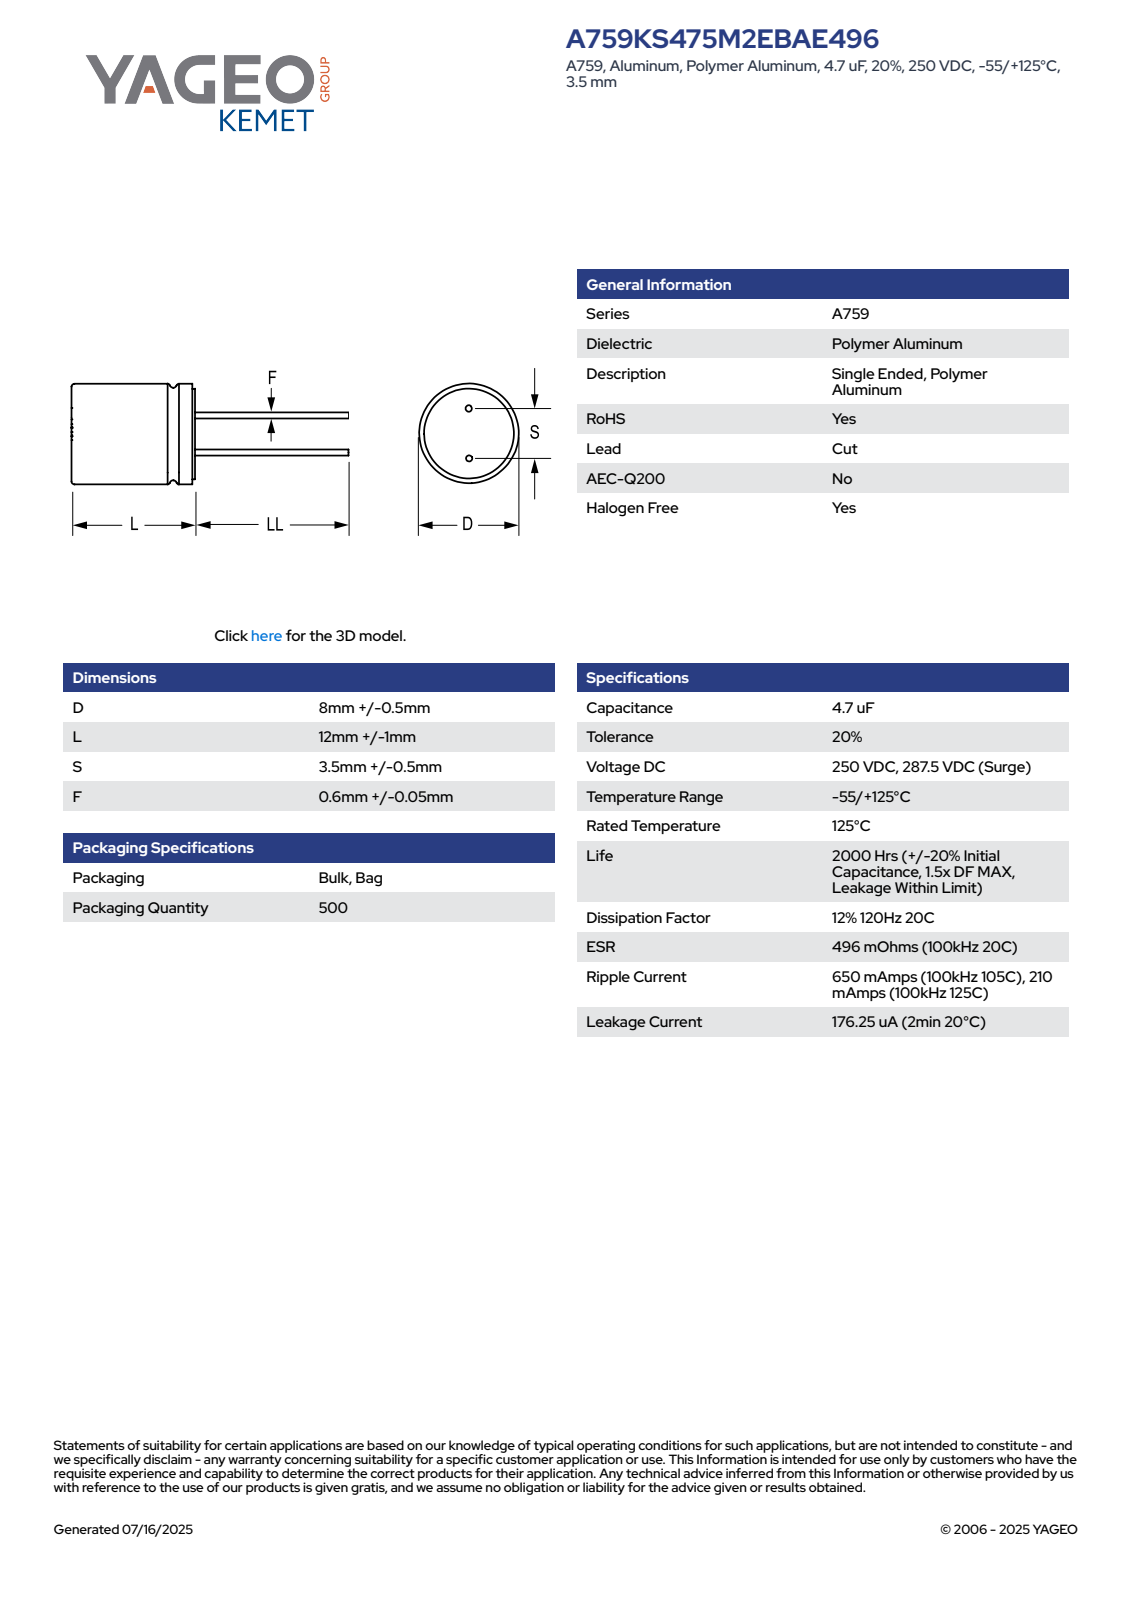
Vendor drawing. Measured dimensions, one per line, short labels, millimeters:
name: CAR_KPC_8X12_D8.5L13S3.5LL5.5F0.65
written by: SolidWorks 2014 (AUTOMOTIVE_DESIGN)
unit: mm
bodies: 4 solids, 78 faces (62 planar, 10 cylindrical, 6 other)
size: 18.5 × 8.5 × 8.5
volume: 736 mm³; area: 495 mm²
bosses: 2× ⌀0.65, 1× ⌀8.5, 1× ⌀7.63
face distances: 13, 12.85, 12.86, 13.01, 18.51, 18.5, 5.65, 5.5, 1.09, 0.88
